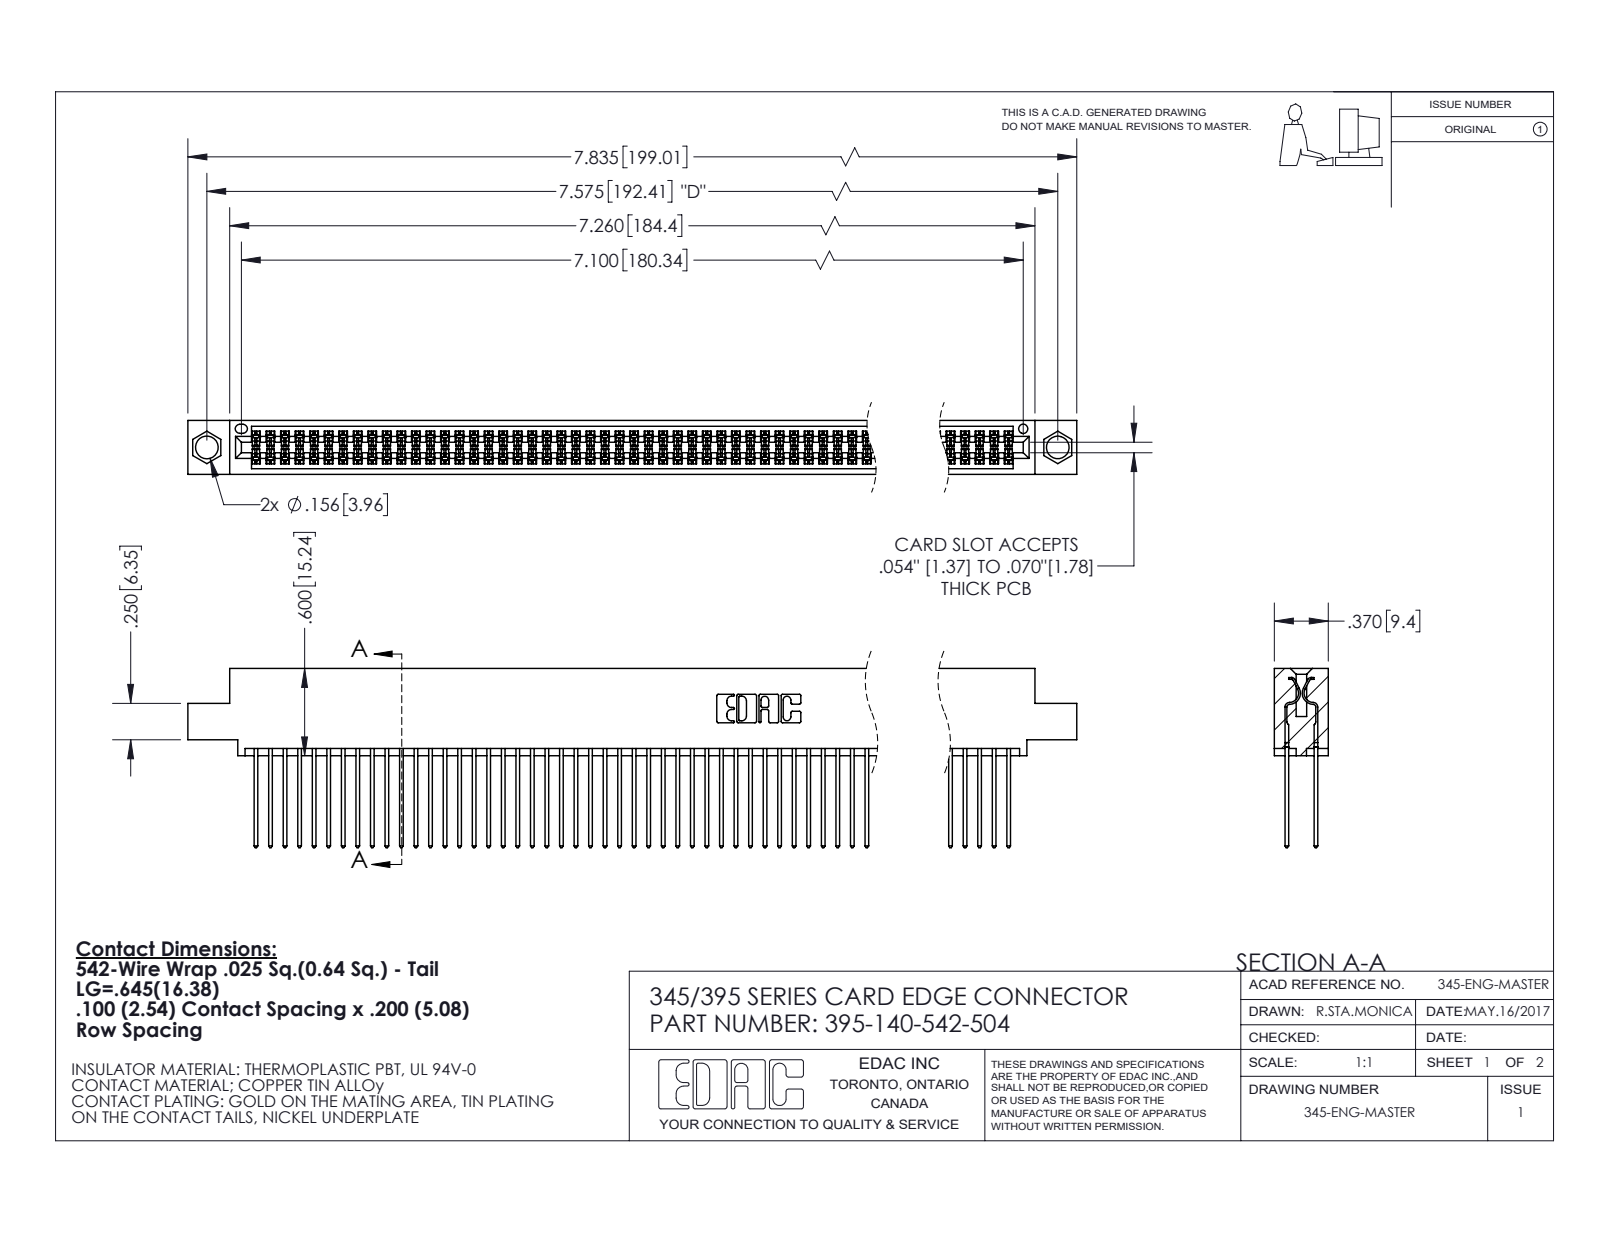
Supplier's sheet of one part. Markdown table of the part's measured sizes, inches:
| quantity | value |
| --- | --- |
| part name | 395-140-542-504; 345-292-001_345-293-142; 345 Part_0.110 Offset - 0.156 Dia-TI |
| STEP written by | SolidWorks 2020 (CONFIG_CONTROL_DESIGN) |
| units | inches |
| bodies | 141 solids, 7144 faces (4718 planar, 2426 cylindrical, 0 other) |
| overall size | 7.835 × 1.232 × 0.37 |
| volume | 1.224 in³ |
| surface area | 51.45 in² |
| round holes (diameter × count) | 0.156 × 2, 0.064 × 1 |
| partial cylindrical surfaces (radius × count) | 0.006 × 210, 0.01 × 140, 0.01 × 22, 0.007 × 6, 0.031 × 6, 0.026 × 3, 0.014 × 2, 0.019 × 2 |
| main face-to-face distances | 0.072, 0.298, 0.2, 0.098, 0.272, 0.025, 0.225, 0.37, 0.175, 0.149 |
| hole center spacings | 0.27, 7.339, 7.575 |
